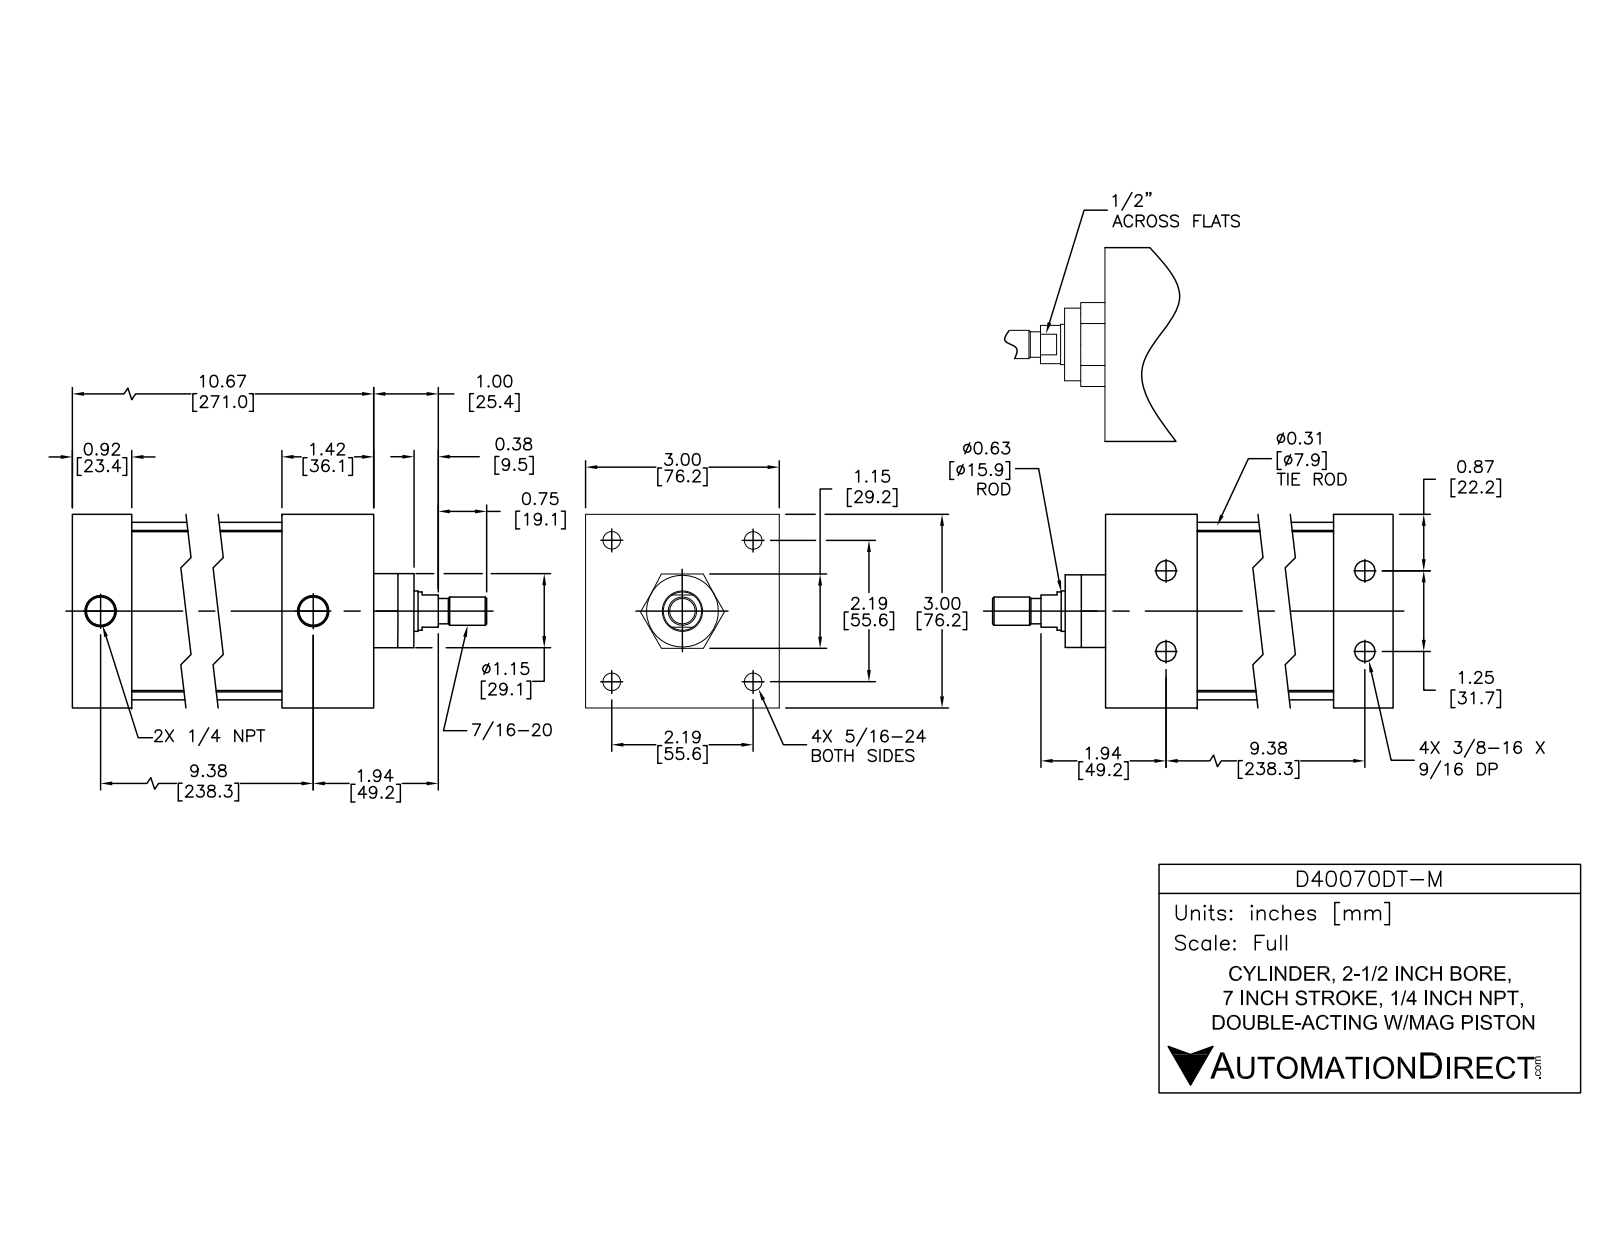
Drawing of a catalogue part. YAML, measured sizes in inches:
part_name: "D40070DT-M; D40070DT-M PISTON; D40070DT-M BODY"
step_written_by: "SolidWorks 2015 (AUTOMOTIVE_DESIGN)"
units: inches
bodies: {solids: 12, faces: 298, planar: 94, cylindrical: 114, other: 90}
overall_size: [12.496, 3, 3]
volume: 40.3
surface_area: 306.6
round_holes:
  - {diameter: 0.267, count: 4}
  - {diameter: 0.307, count: 4}
  - {diameter: 0.359, count: 4}
  - {diameter: 0.5, count: 4}
  - {diameter: 0.297, count: 2}
  - {diameter: 0.477, count: 2}
  - {diameter: 0.625, count: 1}
  - {diameter: 0.628, count: 1}
  - {diameter: 2.5, count: 1}
round_bosses_or_shafts:
  - {diameter: 0.484, count: 4}
  - {diameter: 0.313, count: 4}
  - {diameter: 0.282, count: 4}
  - {diameter: 2.75, count: 1}
  - {diameter: 2.497, count: 1}
  - {diameter: 1.12, count: 1}
  - {diameter: 0.622, count: 1}
  - {diameter: 0.59, count: 1}
partial_cylinders:
  - {radius: 0.3, count: 4}
face_to_face_distances: [3, 0.08, 8.326, 10.746, 9.726, 1.02, 1.42, 8.306, 9.326, 1]
hole_center_spacings: [1.556, 2.2, 9.391, 9.37, 0.625, 0.625, 1.25, 3.111]
